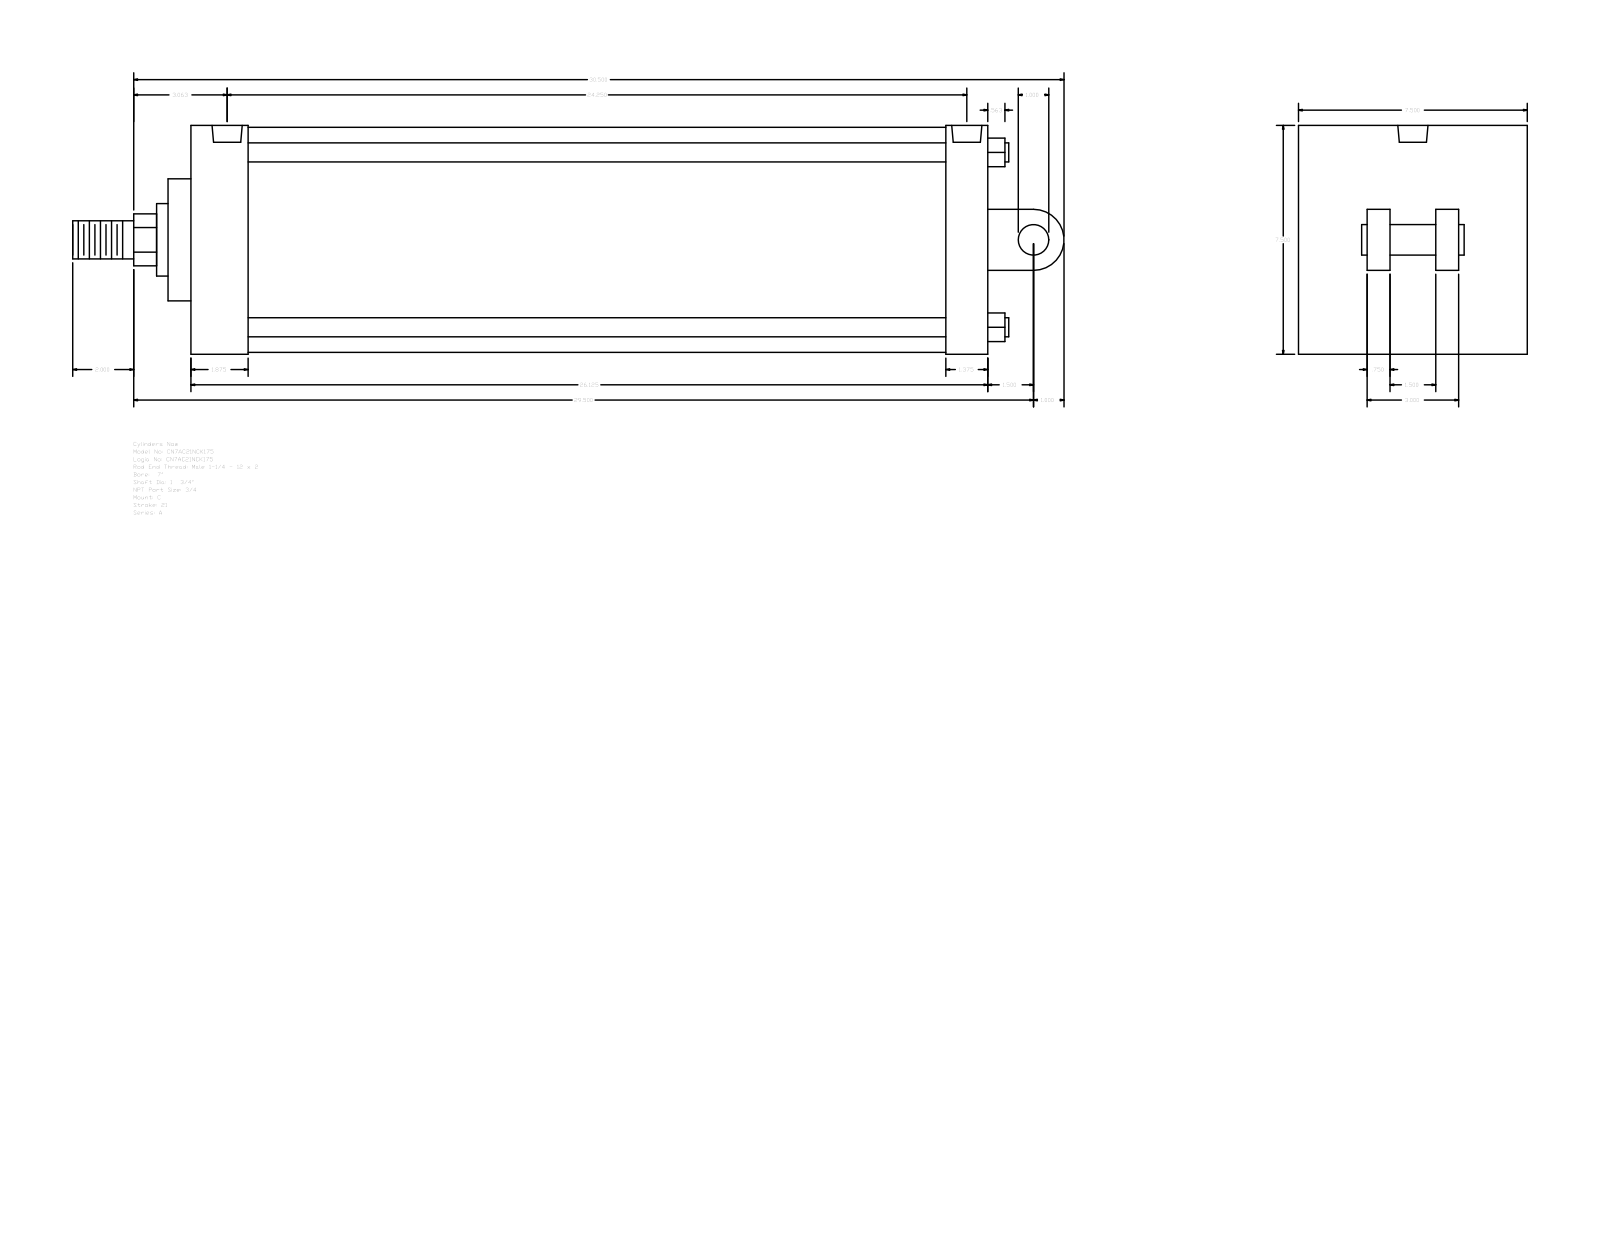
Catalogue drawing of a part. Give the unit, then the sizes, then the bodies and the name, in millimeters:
Units: millimetres
Overall size (bounding box): 825.5 × 190.5 × 190.5
Round holes (diameter × count): ⌀15.08 ×4, ⌀25.12 ×2
Round bosses / shafts (diameter × count): ⌀15.88 ×4, ⌀187.32 ×1, ⌀60.33 ×1, ⌀44.45 ×1, ⌀31.75 ×1, ⌀25.4 ×1
Partial cylindrical surfaces — rounded edges, fillets, slot ends (radius × count): R21.63 ×1, R25.4 ×1
Main face-to-face distances: 190.5, 663.58, 19.05, 76.2, 57.15, 146.05, 44.45, 69.85, 47.63, 615.95
Hole centre spacings: 5.56, 604.83, 610.39, 615.95
Bodies: 0 solids, 104 faces (75 planar, 29 cylindrical, 0 other)
Part name (STEP PRODUCT): A_C__0700_1.75
STEP written by: GSSL Pune (CONFIG_CONTROL_DESIGN)
